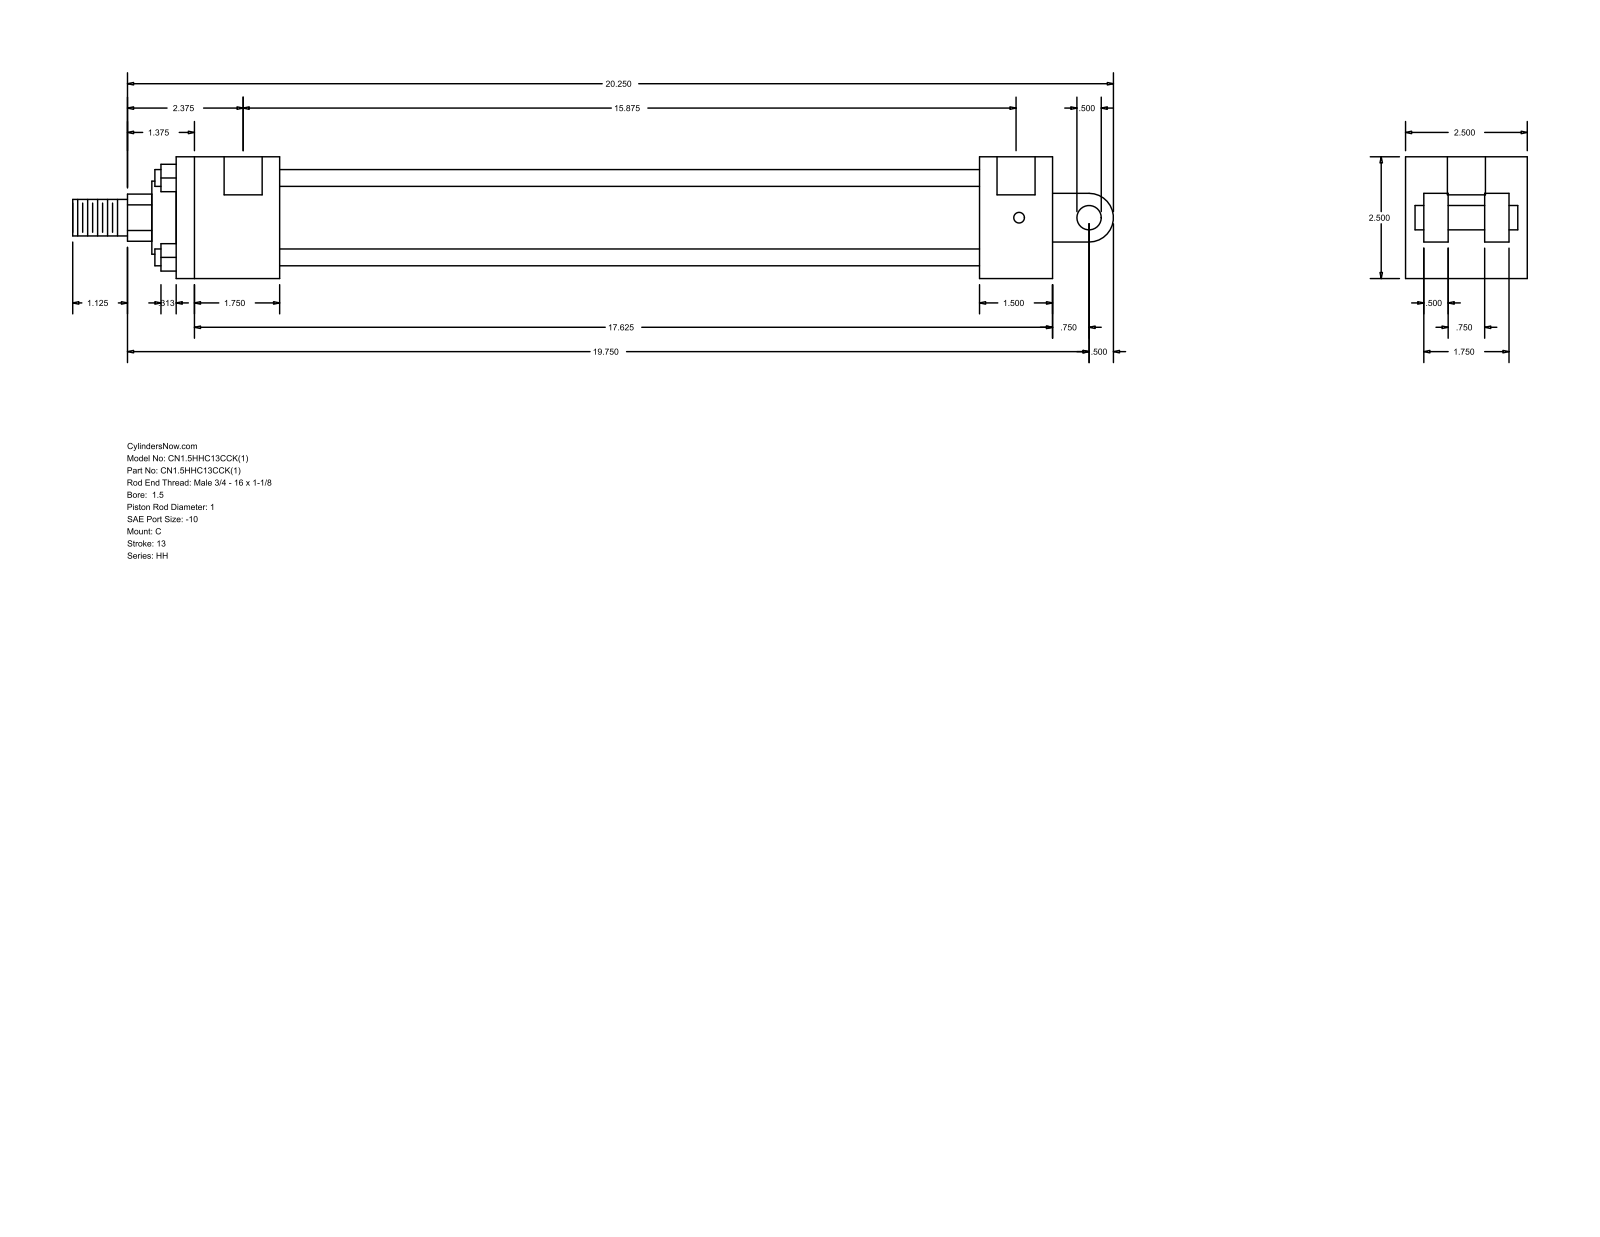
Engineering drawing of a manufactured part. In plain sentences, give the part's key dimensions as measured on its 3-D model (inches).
The part is named "HH_C__0150_1". Its 3-D file was written by "GSSL Pune (CONFIG_CONTROL_DESIGN)". It is 0 solids with 99 faces: 70 planar, 29 cylindrical and 0 other. Overall it measures 21.375 by 2.5 by 2.5 inches. Round holes: 4 of diameter 0.219, 2 of diameter 0.781. Round bosses or shafts: 4 of diameter 0.345, 1 of diameter 1.75, 1 of diameter 1.5, 1 of diameter 1, 1 of diameter 0.75, 1 of diameter 0.5. Partial cylindrical surfaces (rounded edges, fillets, slot ends): 1 of radius 0.484, 1 of radius 0.5. The main face-to-face distances are 2.5, 2.125, 1.5, 14.375, 15.875, 16.5, 18, 0.5, 0.375, 0.875. The hole center spacings are 0.063, 15.937, 16, 15.875.
